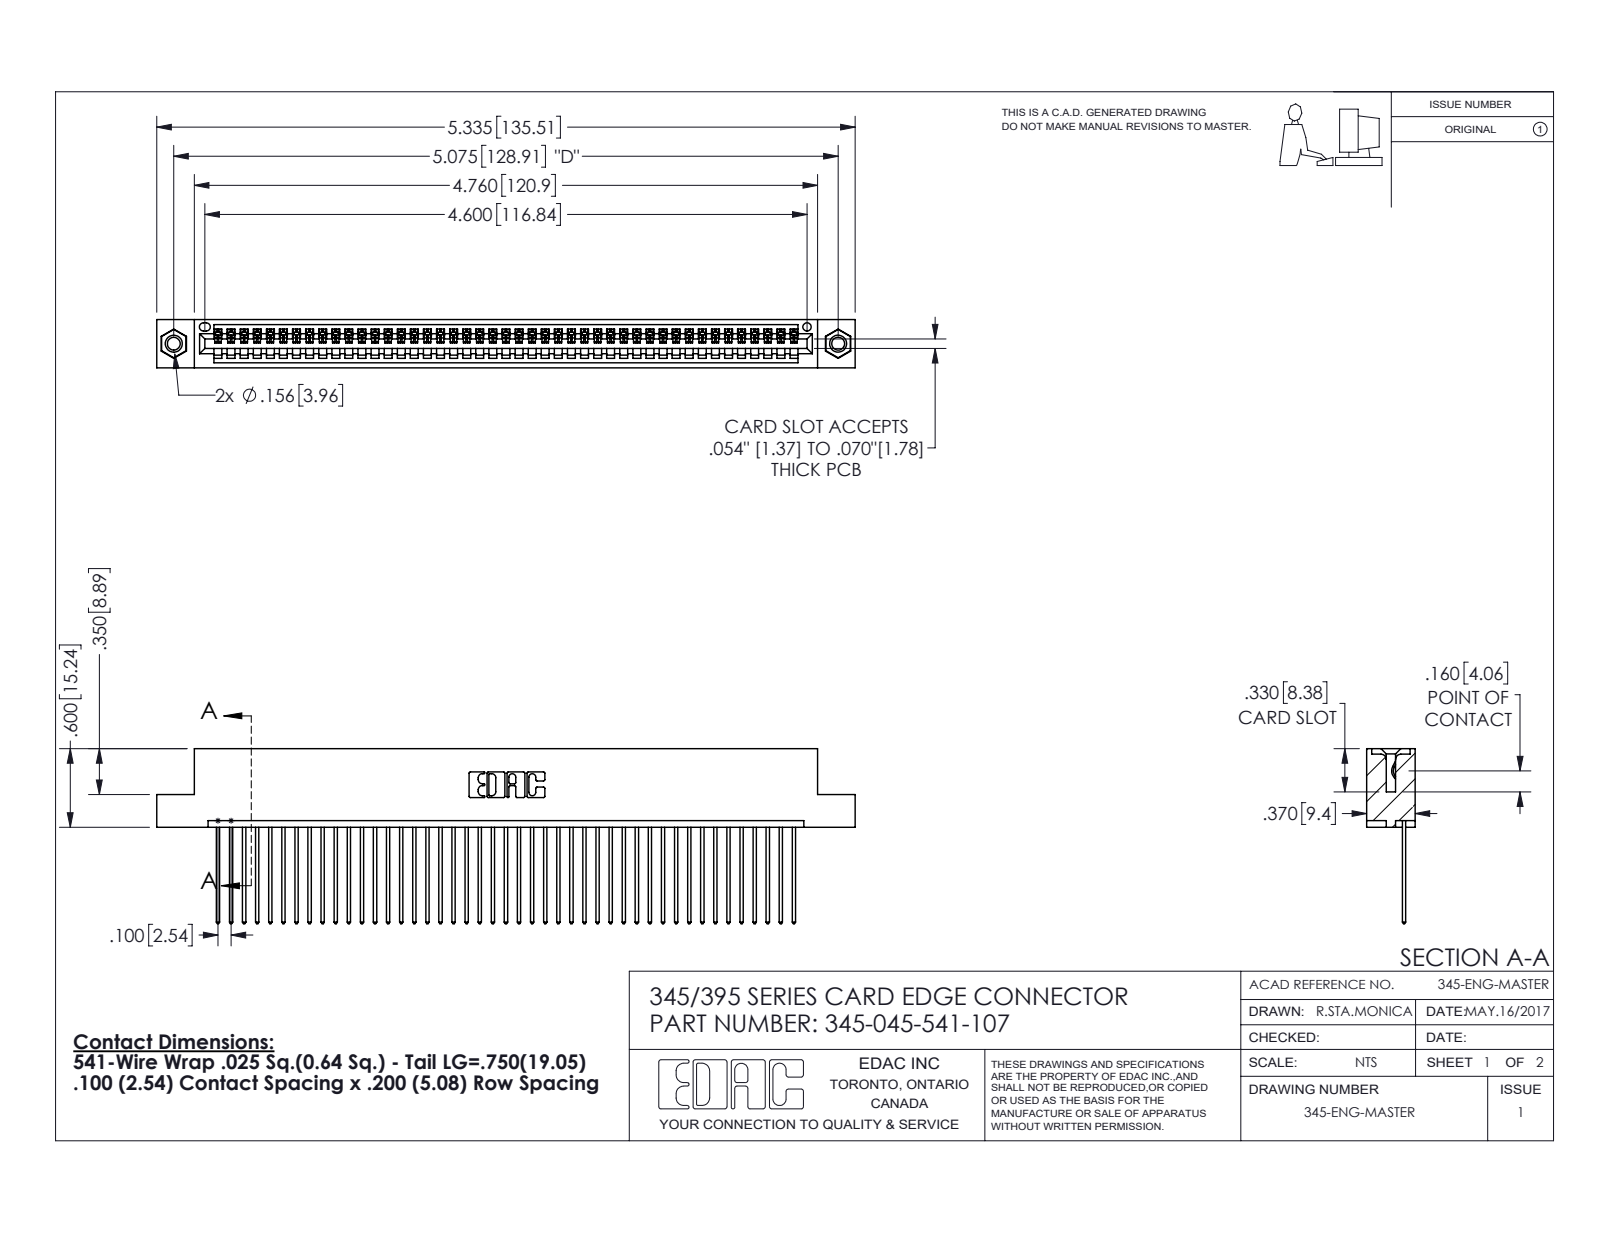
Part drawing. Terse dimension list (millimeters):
name: 345-250-001_345-250-005-103; 345-045-541-107; 345-292-001_345-293-141; 345 Part_Flush Mounting Lugs - 0.156 Dia-TI
written by: SolidWorks 2016 (CONFIG_CONTROL_DESIGN)
unit: mm
bodies: 48 solids, 2796 faces (1912 planar, 868 cylindrical, 16 other)
size: 135.5 × 34 × 9.4
volume: 13 000 mm³; area: 18 260 mm²
holes: 2× ⌀2.5, 2× ⌀3.2, 2× ⌀4, 1× ⌀1.6
bosses: 2× ⌀3.9
rounds: 90× R0.2, 90× R0.3, 22× R0.3, 6× R0.2, 6× R0.8, 3× R0.7, 2× R0.8, 2× R1
face distances: 1.8, 7.6, 2.5, 6.9, 0.6, 9.4, 5.1, 5.7, 3.8, 1.8
hole spacings: 6.9, 122.9, 128.9
